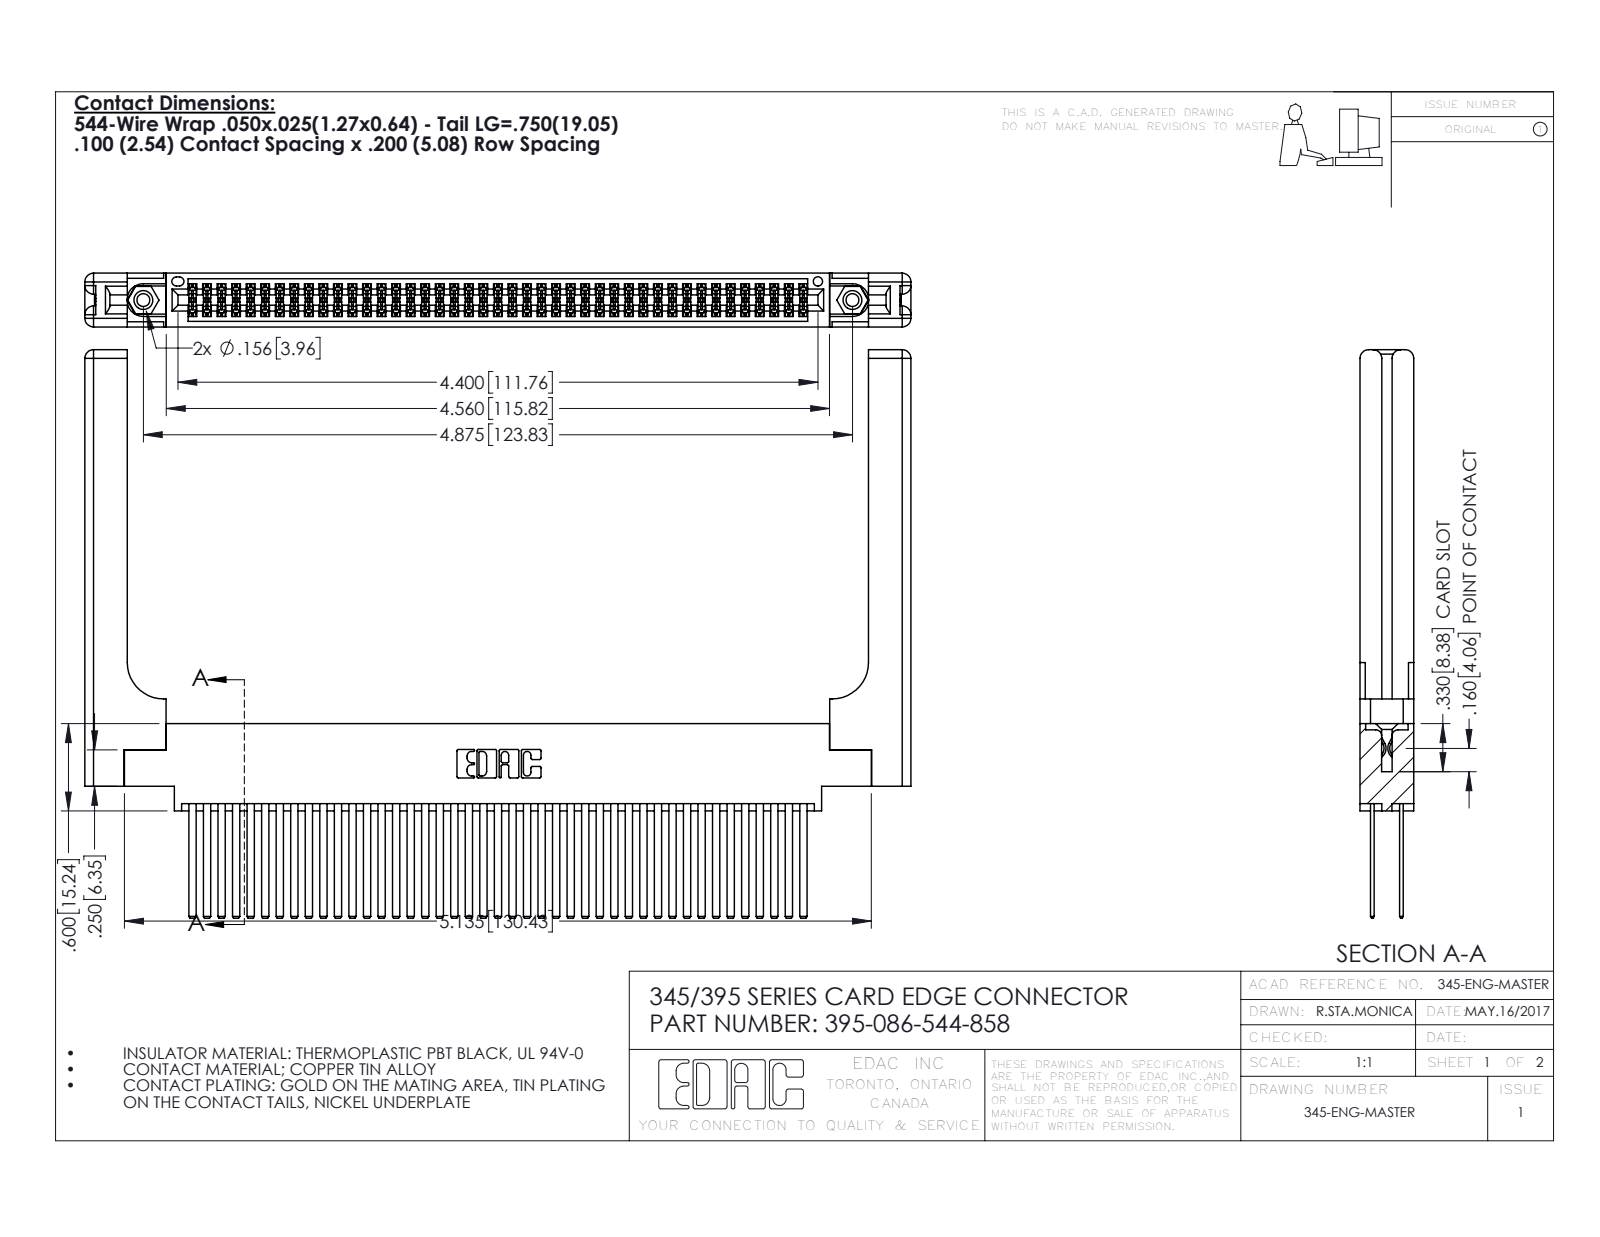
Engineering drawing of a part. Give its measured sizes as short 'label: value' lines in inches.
name: 345 Part_0.170 Offset - 0.156 Dia-TH; 345-292-001_345-293-144; 395-086-544-858; 345-220-058_345-220-058 (+1 more)
written by: SolidWorks 2016 (CONFIG_CONTROL_DESIGN)
unit: in
bodies: 91 solids, 4170 faces (2726 planar, 1384 cylindrical, 60 other)
size: 5.679 × 3.907 × 0.37
volume: 1.439 in³; area: 48.2 in²
holes: 2× ⌀0.089, 2× ⌀0.125, 2× ⌀0.156, 1× ⌀0.064
bosses: 2× ⌀0.155
rounds: 129× R0.006, 22× R0.01, 16× R0.06, 6× R0.007, 6× R0.031, 3× R0.026, 2× R0.014, 2× R0.019
face distances: 0.072, 0.298, 0.098, 0.272, 0.025, 0.2, 0.37, 0.225, 0.175, 0.148
hole spacings: 0.27, 4.639, 4.875
